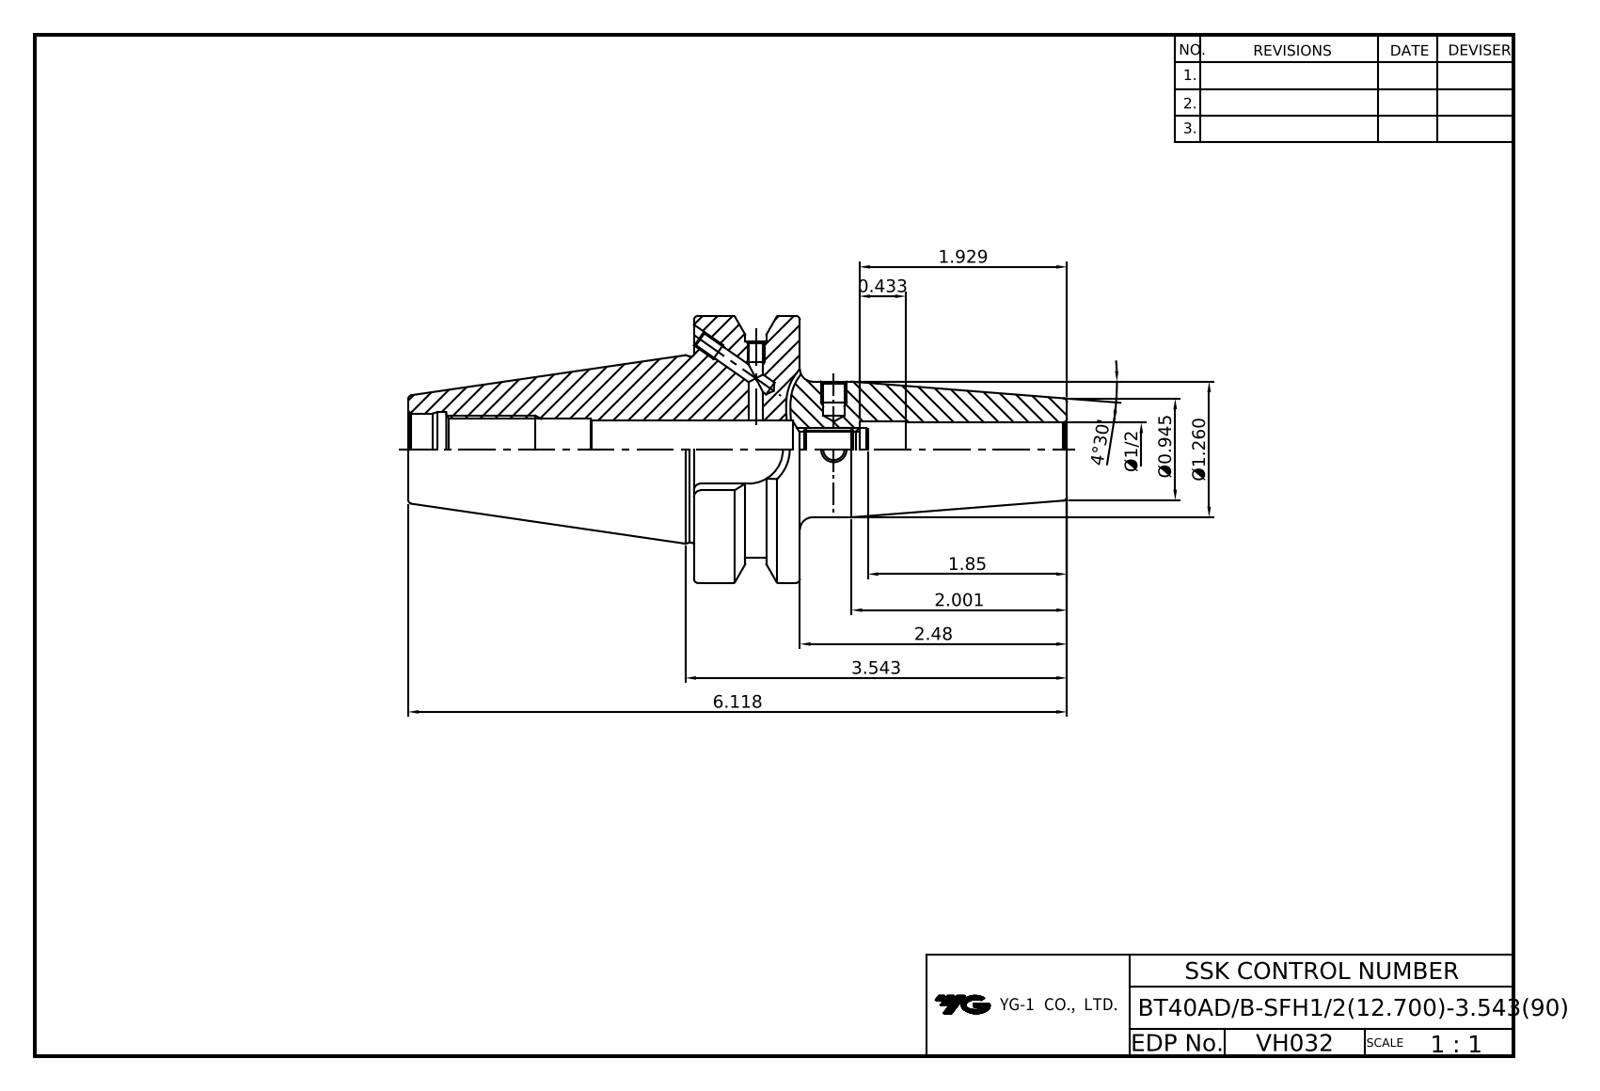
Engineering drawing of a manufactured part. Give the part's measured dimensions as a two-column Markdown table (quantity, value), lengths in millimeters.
| quantity | value |
| --- | --- |
| part name | BT40ADB-SFH9_525-90 |
| STEP written by | CREO PARAMETRIC BY PTC INC, 2018500 (CONFIG_CONTROL_DESIGN) |
| units | millimeters |
| bodies | 1 solid, 92 faces (22 planar, 30 cylindrical, 40 other) |
| overall size | 155.4 × 63 × 63 |
| volume | 153 423 mm³ |
| surface area | 31 867 mm² |
| round holes (diameter × count) | 9 × 1, 10 × 1, 12.7 × 1, 13.3 × 1, 13.5 × 1, 14 × 1, 16 × 1, 17 × 1, 17.6 × 1 |
| round bosses / shafts (diameter × count) | 63 × 1, 51 × 1, 44 × 1, 32 × 1 |
| partial cylindrical surfaces (radius × count) | 8.05 × 1 |
| main face-to-face distances | 25, 45.2, 17.1, 7.9, 88, 70.9, 63, 12.1, 5, 12.9 |
